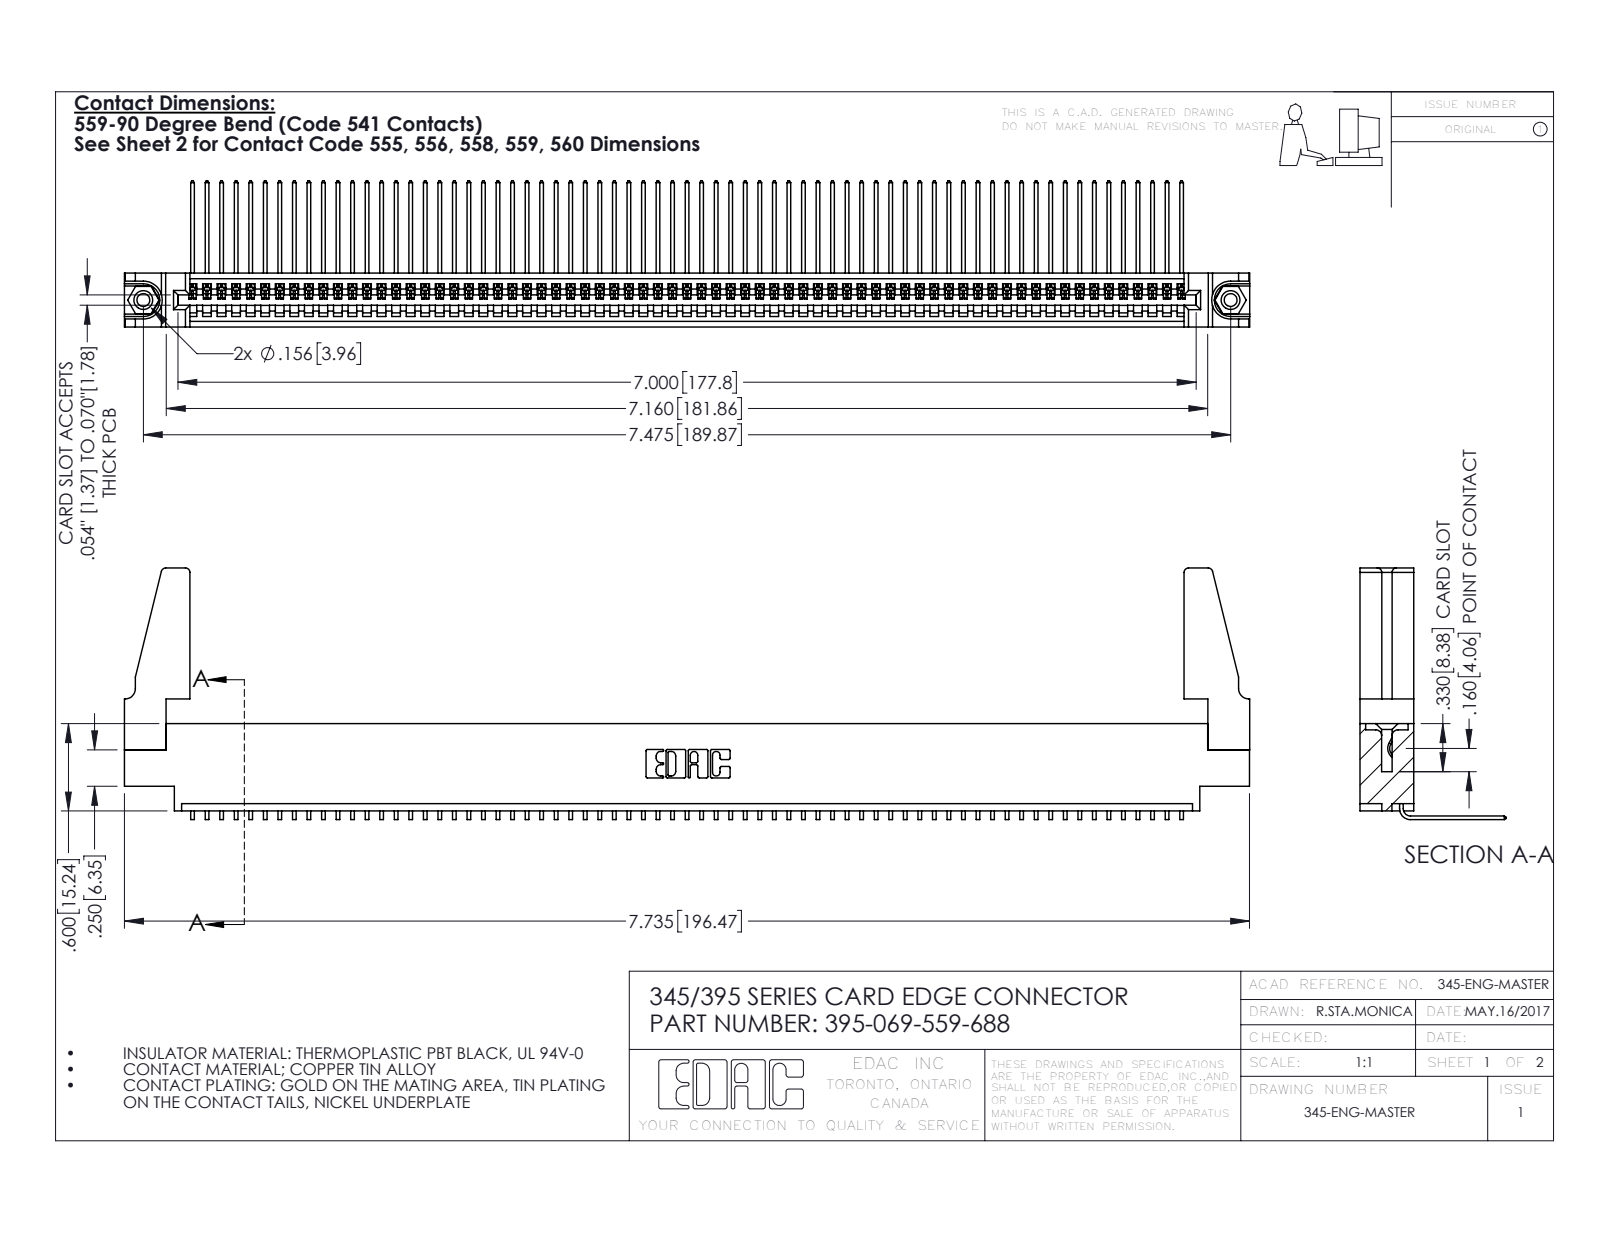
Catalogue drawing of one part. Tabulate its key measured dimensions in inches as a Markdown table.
| quantity | value |
| --- | --- |
| part name | 345-292-001_558 559 Tail - 1; 395-069-559-688; 345-220-078_345-220-088; 345 Part_0.170 Offset - 0.156 Dia-TH (+1 more) |
| STEP written by | SolidWorks 2016 (CONFIG_CONTROL_DESIGN) |
| units | inches |
| bodies | 74 solids, 4394 faces (3054 planar, 1324 cylindrical, 16 other) |
| overall size | 7.736 × 1.729 × 1.005 |
| volume | 1.358 in³ |
| surface area | 46.85 in² |
| round holes (diameter × count) | 0.089 × 2, 0.125 × 2, 0.156 × 2, 0.064 × 1 |
| round bosses / shafts (diameter × count) | 0.155 × 2 |
| partial cylindrical surfaces (radius × count) | 0.006 × 138, 0.01 × 22, 0.03 × 8, 0.007 × 6, 0.031 × 6, 0.026 × 3, 0.031 × 2, 0.04 × 2 |
| main face-to-face distances | 0.072, 0.298, 0.37, 0.098, 0.272, 0.025, 0.2, 0.225, 0.175, 0.149 |
| hole center spacings | 0.27, 7.239, 7.475 |
